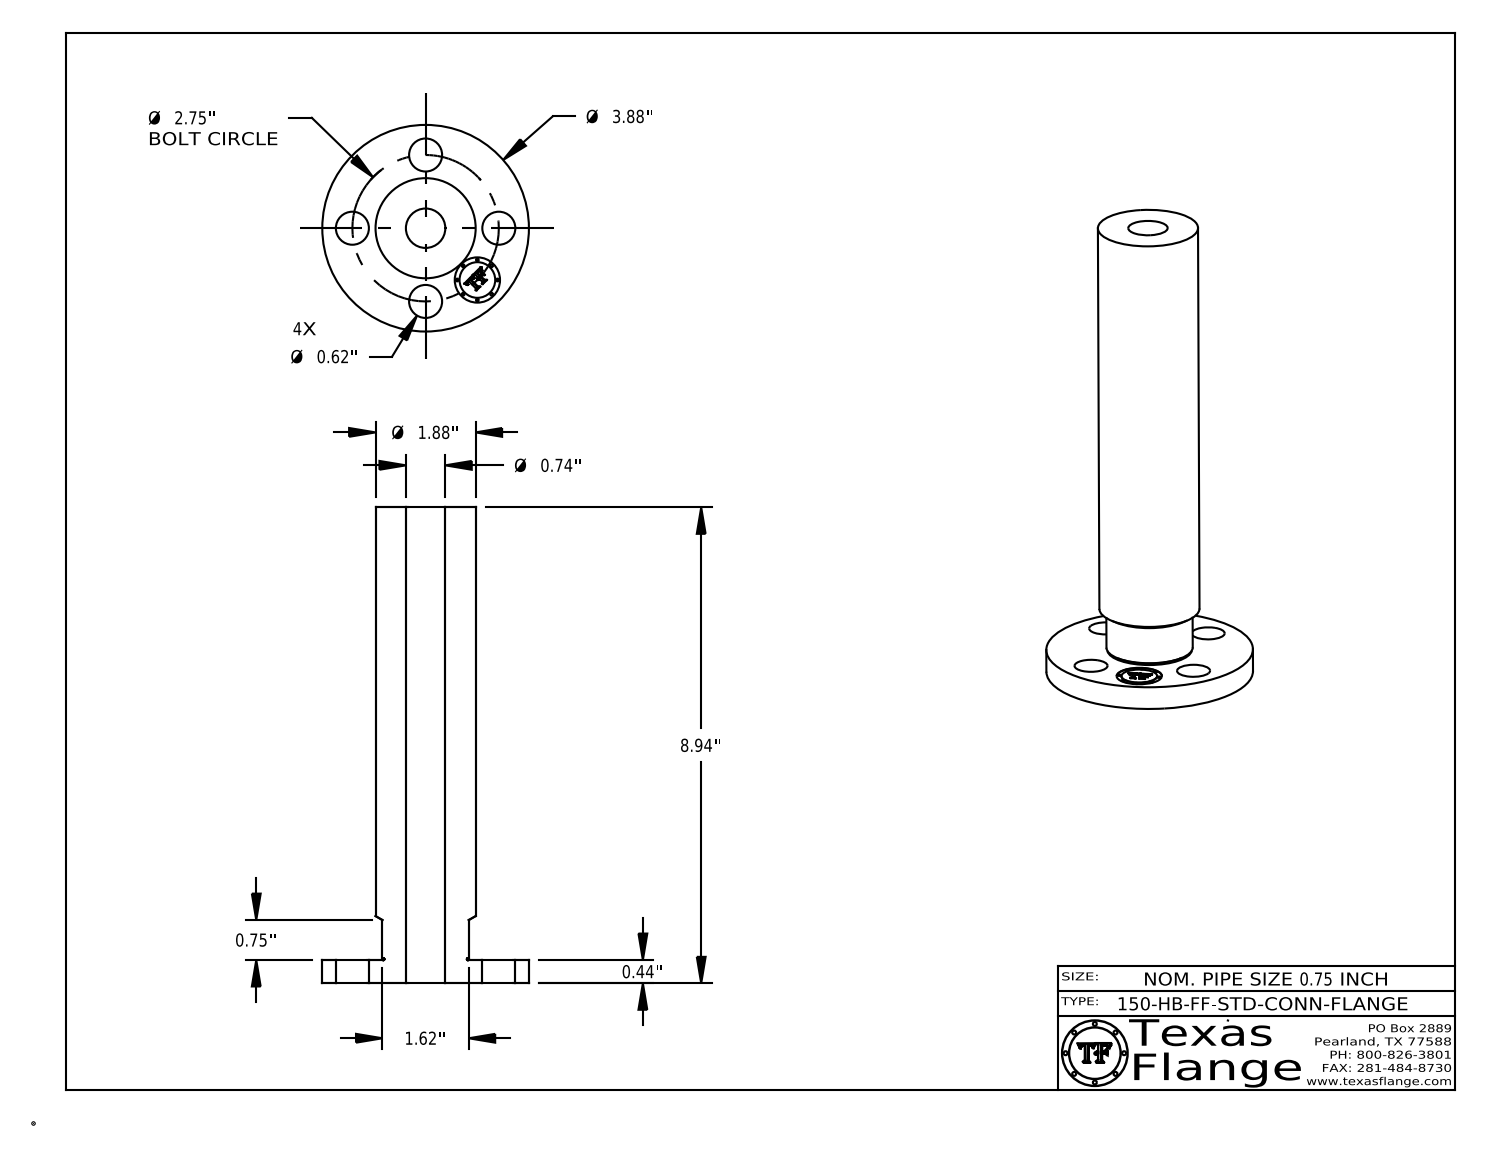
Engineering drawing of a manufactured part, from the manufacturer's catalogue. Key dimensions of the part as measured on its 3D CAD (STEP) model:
Part name (STEP PRODUCT): 0.75-150-HB-FF-STD-CONN-FLANGE
STEP written by: CATIA V5 STEP AP214 (AUTOMOTIVE_DESIGN)
Units: inches
Bodies: 1 solid, 410 faces (368 planar, 36 cylindrical, 6 other)
Overall size (bounding box): 8.938 × 3.88 × 3.88
Volume: 23.83 in³ · Surface area: 100.8 in²
Round holes (diameter × count): ⌀0.62 ×4, ⌀0.74 ×1, ⌀0.85 ×1
Round bosses / shafts (diameter × count): ⌀0.051 ×8, ⌀3.88 ×1, ⌀1.88 ×1, ⌀1.62 ×1, ⌀0.67 ×1
Main face-to-face distances: 0.437, 8.937, 8.5, 0.433, 8.505, 0.254, 0.248, 0.016, 0.046, 0.165
Hole centre spacings: 1.375, 1.945, 1.052, 2.541, 2.75
